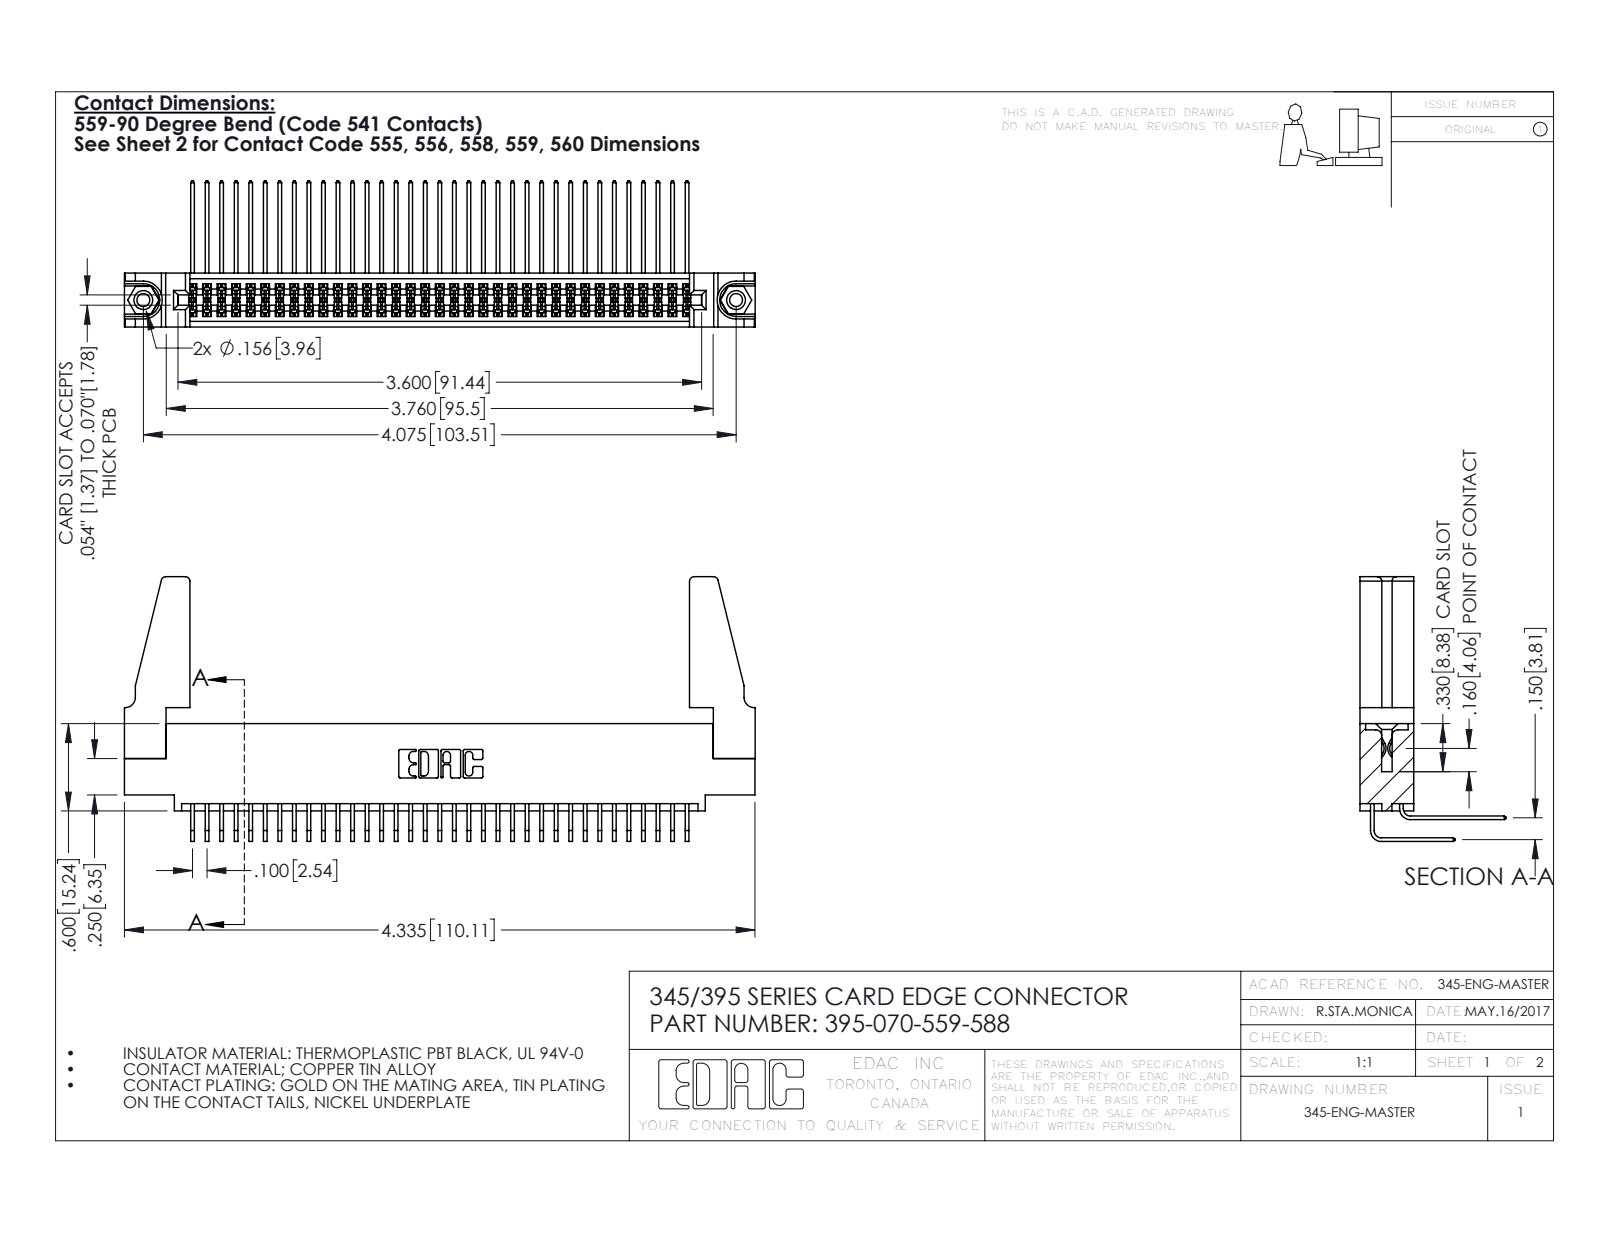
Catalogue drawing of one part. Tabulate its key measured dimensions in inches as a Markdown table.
| quantity | value |
| --- | --- |
| part name | 345-220-078_345-220-088; 345-292-001_559 Tail - 2; 345-292-001_558 559 Tail - 1; 345-250-001_345-250-001-102 (+2 more) |
| STEP written by | SolidWorks 2016 (CONFIG_CONTROL_DESIGN) |
| units | inches |
| bodies | 75 solids, 3894 faces (2606 planar, 1272 cylindrical, 16 other) |
| overall size | 4.336 × 1.819 × 1.005 |
| volume | 0.868 in³ |
| surface area | 32.84 in² |
| round holes (diameter × count) | 0.089 × 2, 0.125 × 2, 0.156 × 2, 0.064 × 1 |
| round bosses / shafts (diameter × count) | 0.155 × 2 |
| partial cylindrical surfaces (radius × count) | 0.006 × 105, 0.01 × 22, 0.03 × 8, 0.007 × 6, 0.031 × 6, 0.026 × 3, 0.014 × 2, 0.019 × 2 |
| main face-to-face distances | 0.072, 0.298, 0.37, 0.2, 0.098, 0.272, 0.025, 0.225, 0.175, 0.15 |
| hole center spacings | 0.27, 3.839, 4.075 |
